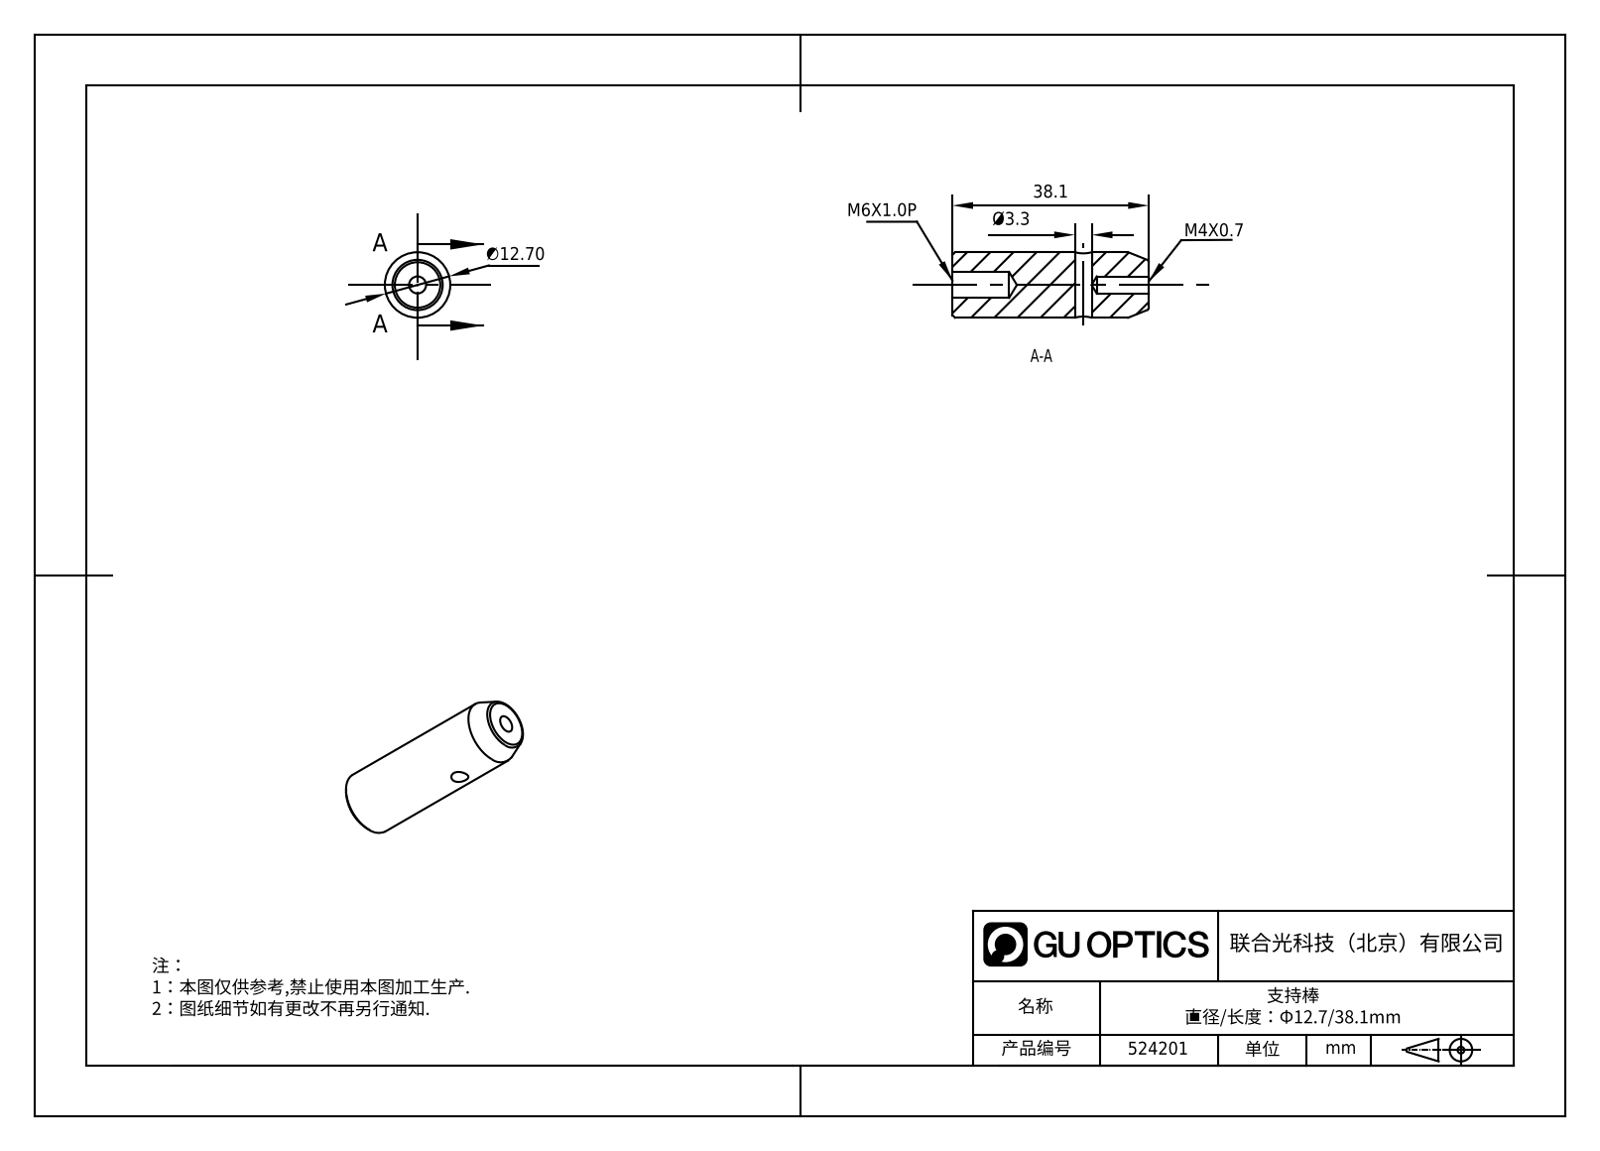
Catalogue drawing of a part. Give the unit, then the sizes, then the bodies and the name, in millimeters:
Units: millimetres
Overall size (bounding box): 38.1 × 12.7 × 12.7
Round holes (diameter × count): ⌀3.3 ×2, ⌀5 ×1
Round bosses / shafts (diameter × count): ⌀12.7 ×1
Main face-to-face distances: 38.1
Volume: 4 281 mm³ · Surface area: 2 088 mm²
Bodies: 1 solid, 20 faces (2 planar, 8 cylindrical, 10 other)
Part name (STEP PRODUCT): 524201
STEP written by: SolidWorks 2016 (AUTOMOTIVE_DESIGN)
